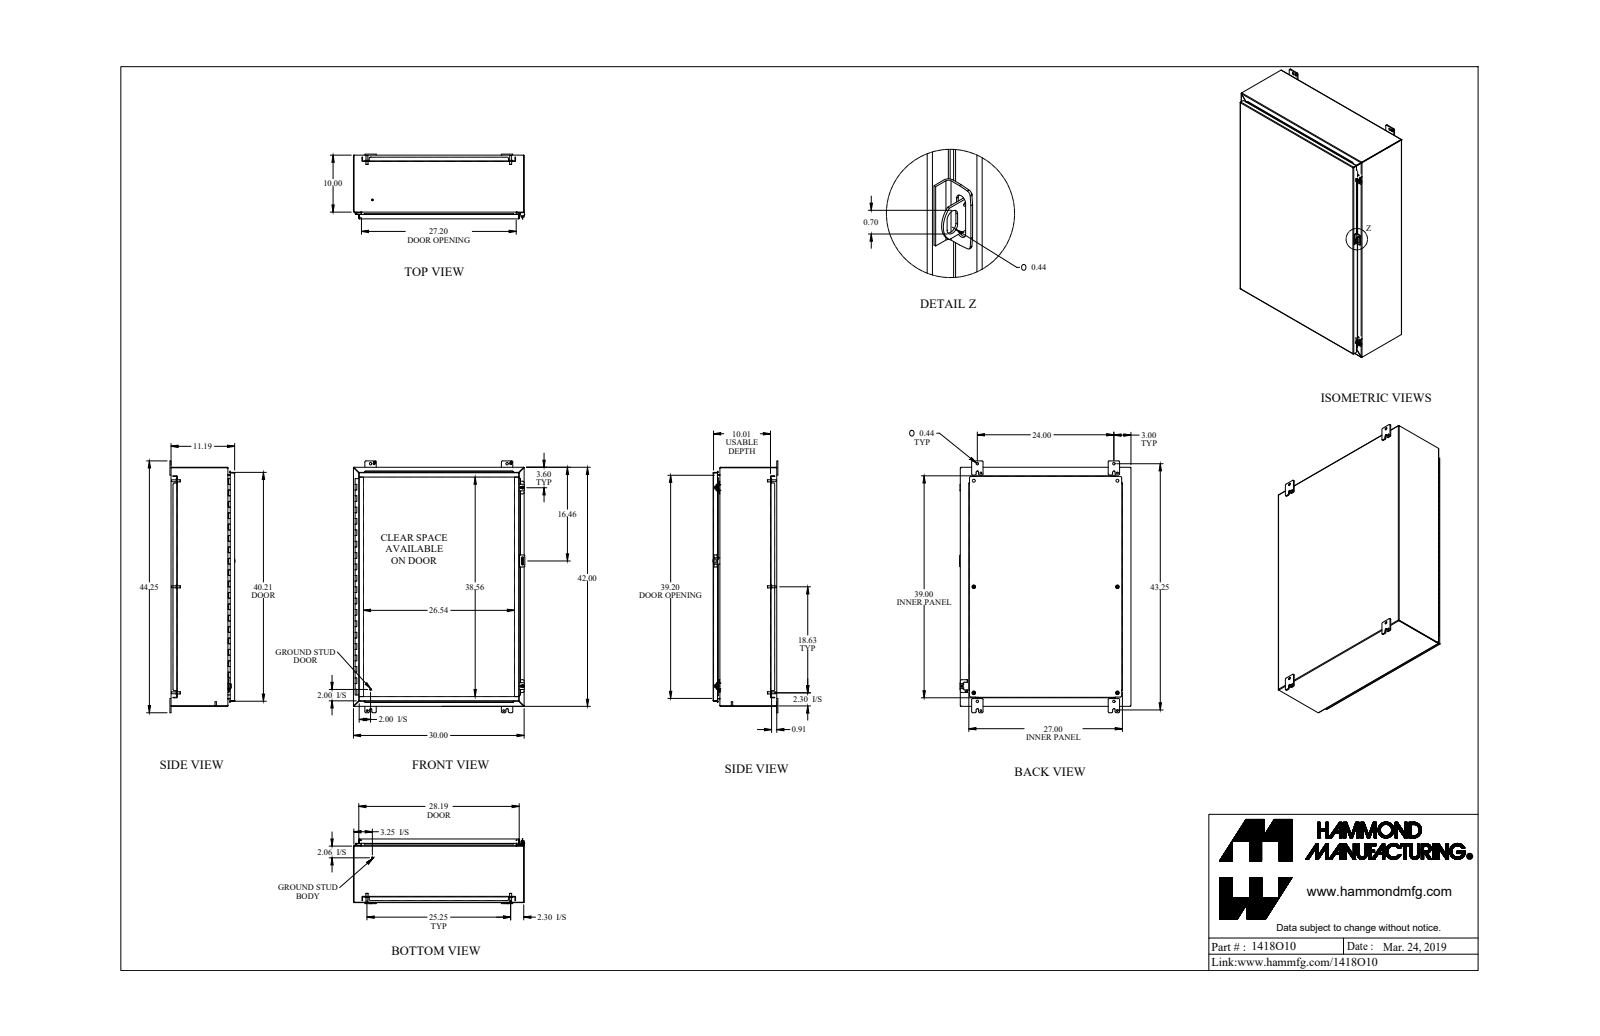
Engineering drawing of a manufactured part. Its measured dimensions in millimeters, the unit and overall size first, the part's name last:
Units: millimetres
Overall size (bounding box): 1124 × 765.2 × 290.5
Round holes (diameter × count): ⌀12.7 ×6, ⌀7.8 ×4, ⌀8 ×4, ⌀11.1 ×4, ⌀11.3 ×4, ⌀5.4 ×2, ⌀6.7 ×2, ⌀9.5 ×2, ⌀3.2 ×1, ⌀4.7 ×1
Round bosses / shafts (diameter × count): ⌀16.5 ×6, ⌀9.5 ×6, ⌀8.4 ×6, ⌀25.4 ×4, ⌀12.7 ×2, ⌀9.9 ×2, ⌀7.1 ×2, ⌀6.4 ×2
Partial cylindrical surfaces — rounded edges, fillets, slot ends (radius × count): R4.8 ×40, R0.9 ×24, R2.7 ×24, R6.4 ×20, R2.9 ×16, R1.2 ×13, R3.6 ×13, R1 ×8
Main face-to-face distances: 1.8, 282.3, 280.4, 284.1, 23.8, 2.4, 25.6, 256.1, 254.2, 26.2
Hole centre spacings: 641.4, 797, 473.1, 609.6, 44.1, 696, 1060.5, 1223.2
Volume: 7 740 000 mm³ · Surface area: 7 919 000 mm²
Bodies: 48 solids, 1523 faces (883 planar, 547 cylindrical, 93 other)
Part name (STEP PRODUCT): 1418O10_Default
STEP written by: SolidWorks 2019 (CONFIG_CONTROL_DESIGN)
